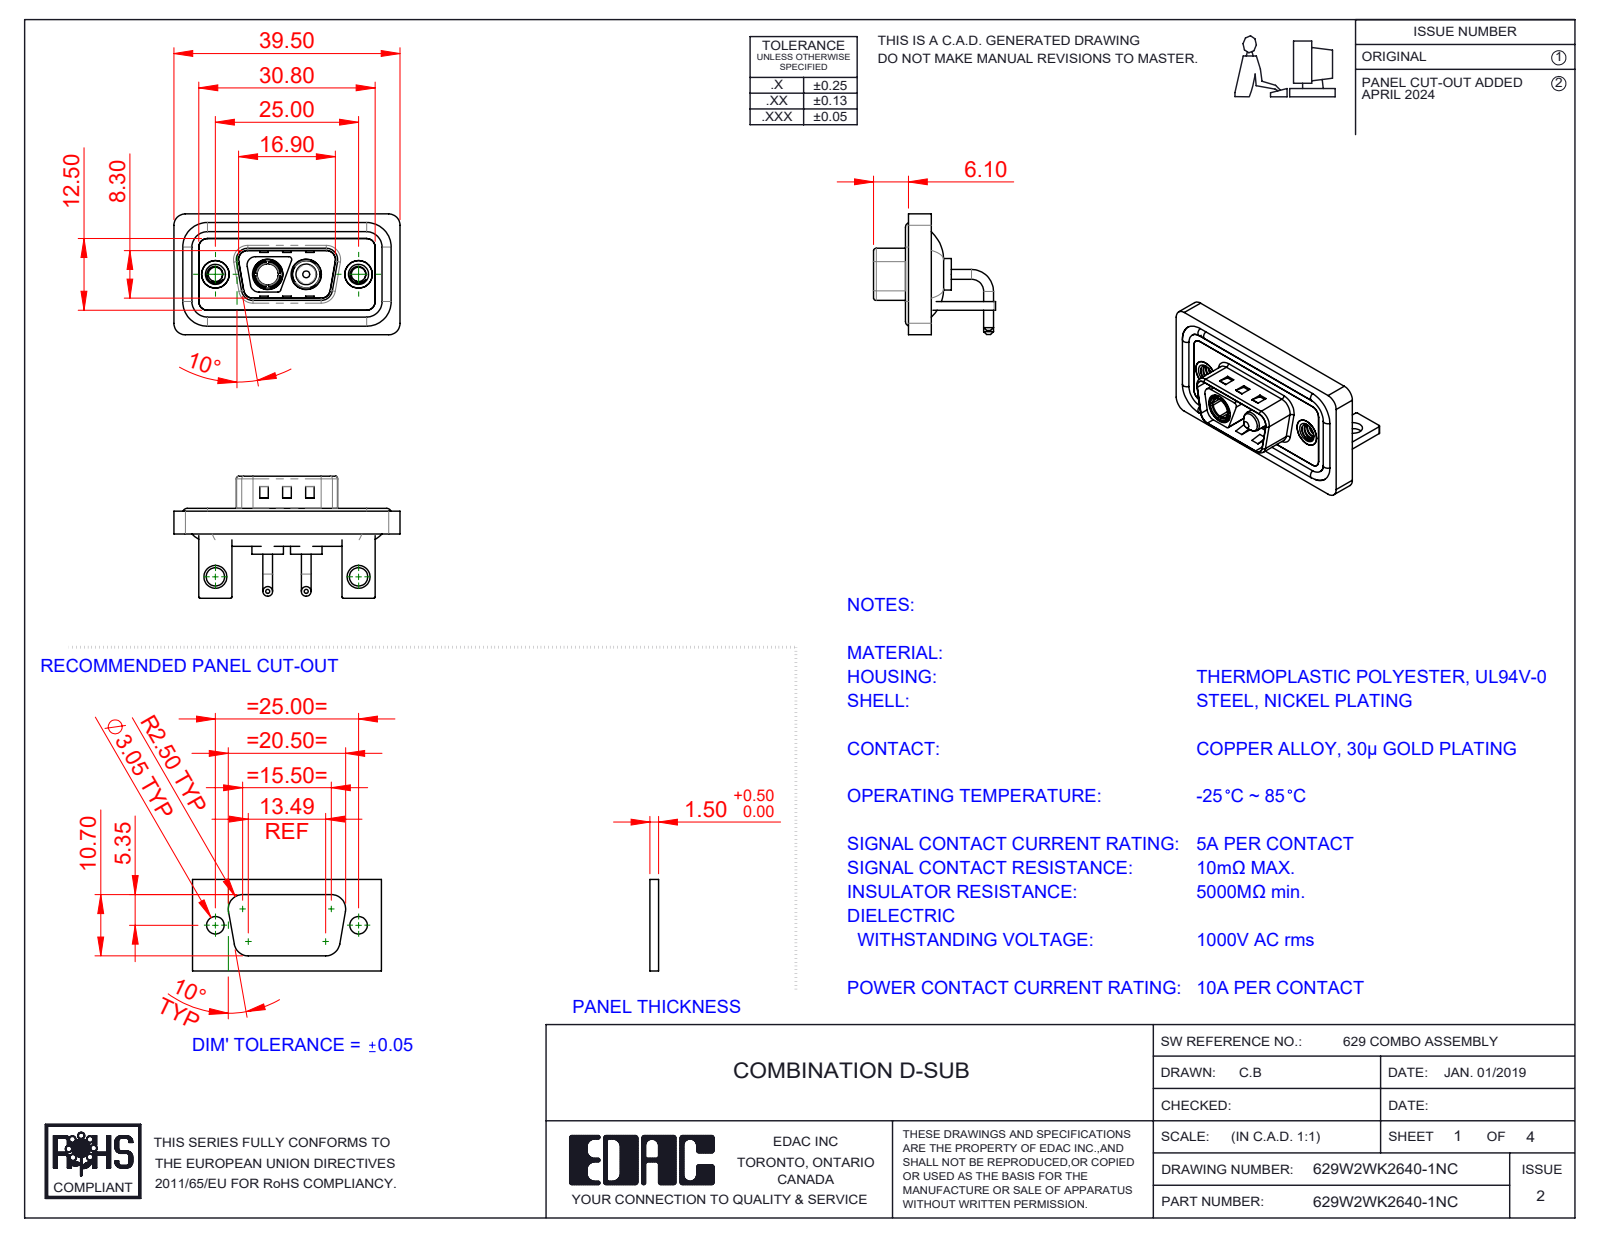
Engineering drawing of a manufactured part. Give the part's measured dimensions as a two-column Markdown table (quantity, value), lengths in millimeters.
| quantity | value |
| --- | --- |
| part name | 629Combo Waterproof Housing_09 Contacts; 629Combo Shell Rear_09 Contacts; 629Combo Shell Front_09 Contacts; 629Combo Threaded Rivet_B (+5 more) |
| STEP written by | SolidWorks 2023 (CONFIG_CONTROL_DESIGN) |
| units | millimeters |
| bodies | 13 solids, 580 faces (209 planar, 249 cylindrical, 122 other) |
| overall size | 39.5 × 21.3 × 21.1 |
| volume | 4 836 mm³ |
| surface area | 8 016 mm² |
| round holes (diameter × count) | 2.5 × 2, 3.2 × 2, 4 × 2, 4.8 × 2, 4.85 × 2, 5 × 2, 5.3 × 2, 3.7 × 1 |
| round bosses / shafts (diameter × count) | 1.7 × 4, 1.6 × 4, 5.5 × 2, 5.2 × 2, 4.9 × 2, 4.75 × 2, 3.75 × 2, 4.96 × 1 |
| partial cylindrical surfaces (radius × count) | 1.5 × 20, 2 × 19, 0.25 × 16, 0.5 × 11, 1.6 × 8, 0.6 × 4, 0.65 × 4, 0.9 × 4 |
| main face-to-face distances | 0.4, 1.5, 2.9, 0.8, 1.1, 1.2, 2.1, 1.6, 3.7, 2.5 |
| hole center spacings | 9.14, 15.86, 25, 6.72 |
